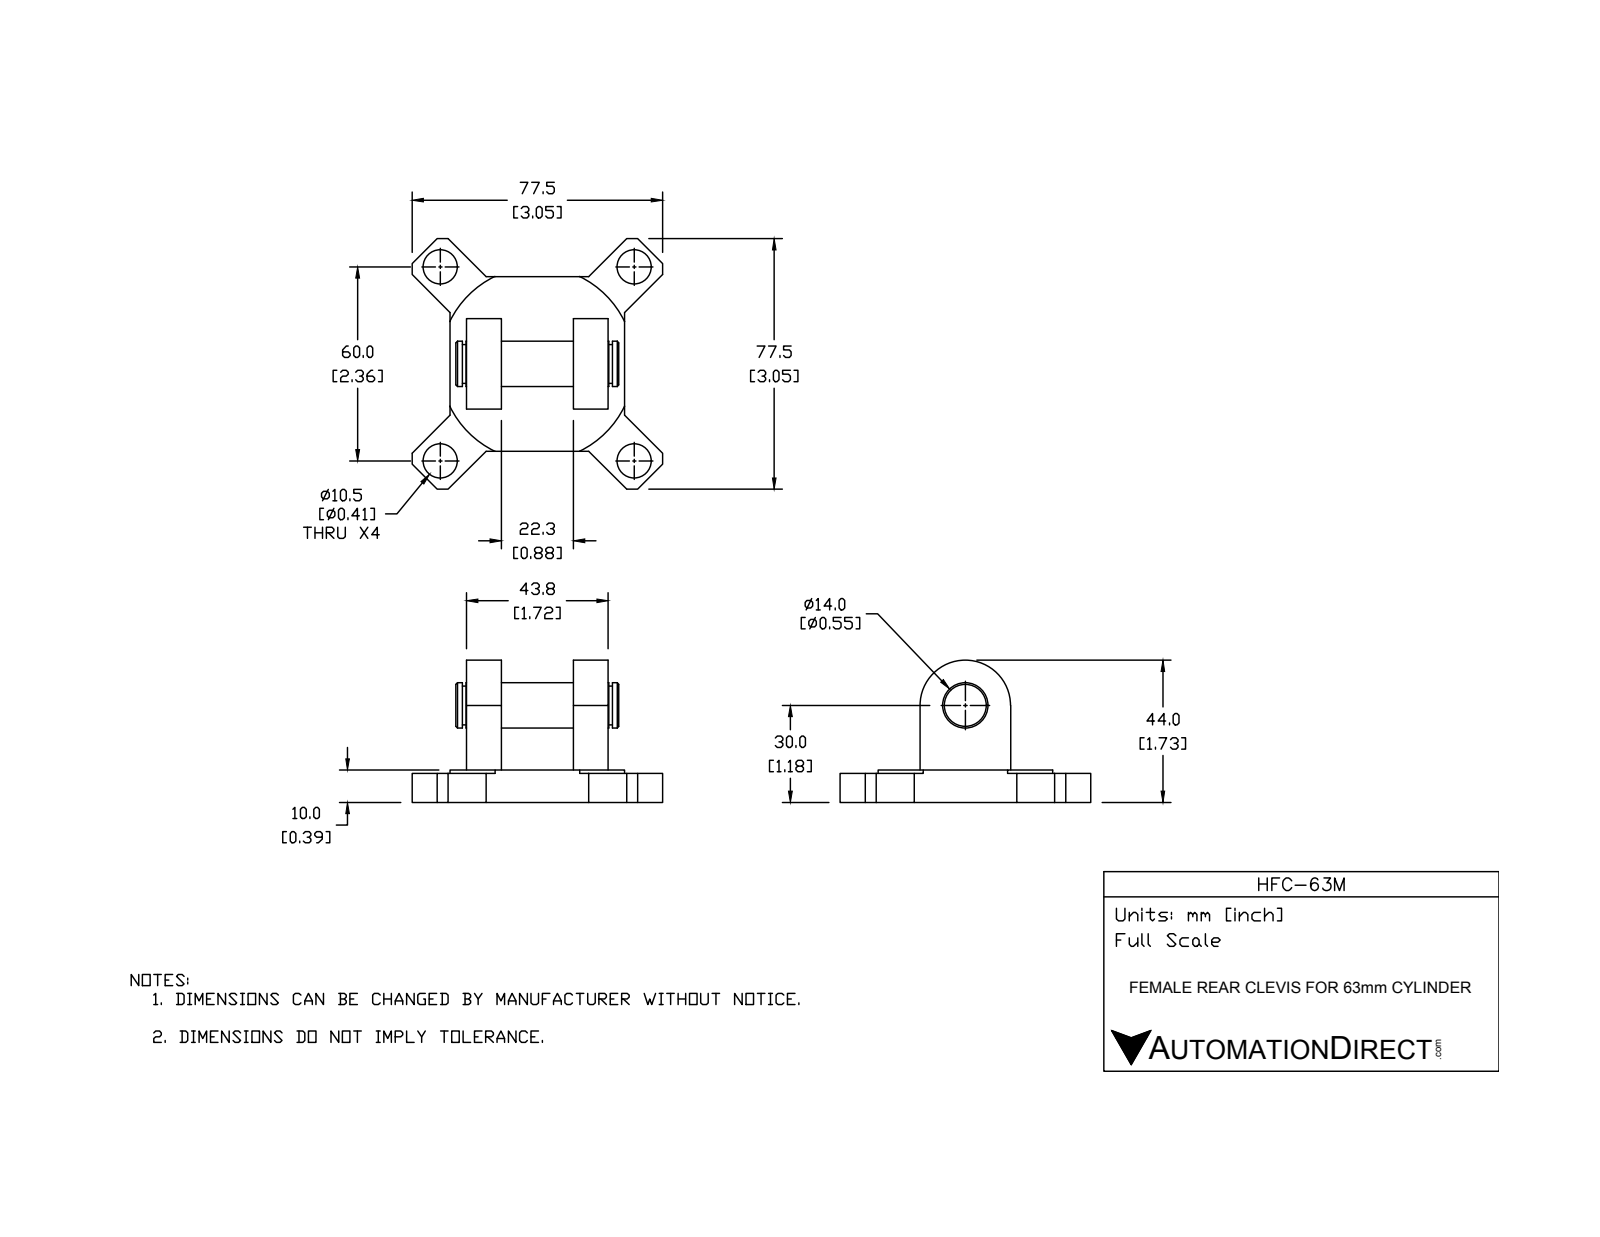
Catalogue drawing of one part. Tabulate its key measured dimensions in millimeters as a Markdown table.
| quantity | value |
| --- | --- |
| part name | HFC-63M |
| STEP written by | SolidWorks 2015 (CONFIG_CONTROL_DESIGN) |
| units | millimeters |
| bodies | 2 solids, 76 faces (44 planar, 28 cylindrical, 4 other) |
| overall size | 77.5 × 77.5 × 44 |
| volume | 57 089 mm³ |
| surface area | 18 994 mm² |
| round holes (diameter × count) | 10.5 × 4 |
| round bosses / shafts (diameter × count) | 14 × 1, 12 × 1 |
| partial cylindrical surfaces (radius × count) | 14 × 1, 30 × 1 |
| main face-to-face distances | 10, 10.75, 33.05, 9, 1, 43.8, 22.3, 13, 41, 5.1 |
| hole center spacings | 60, 84.85 |
